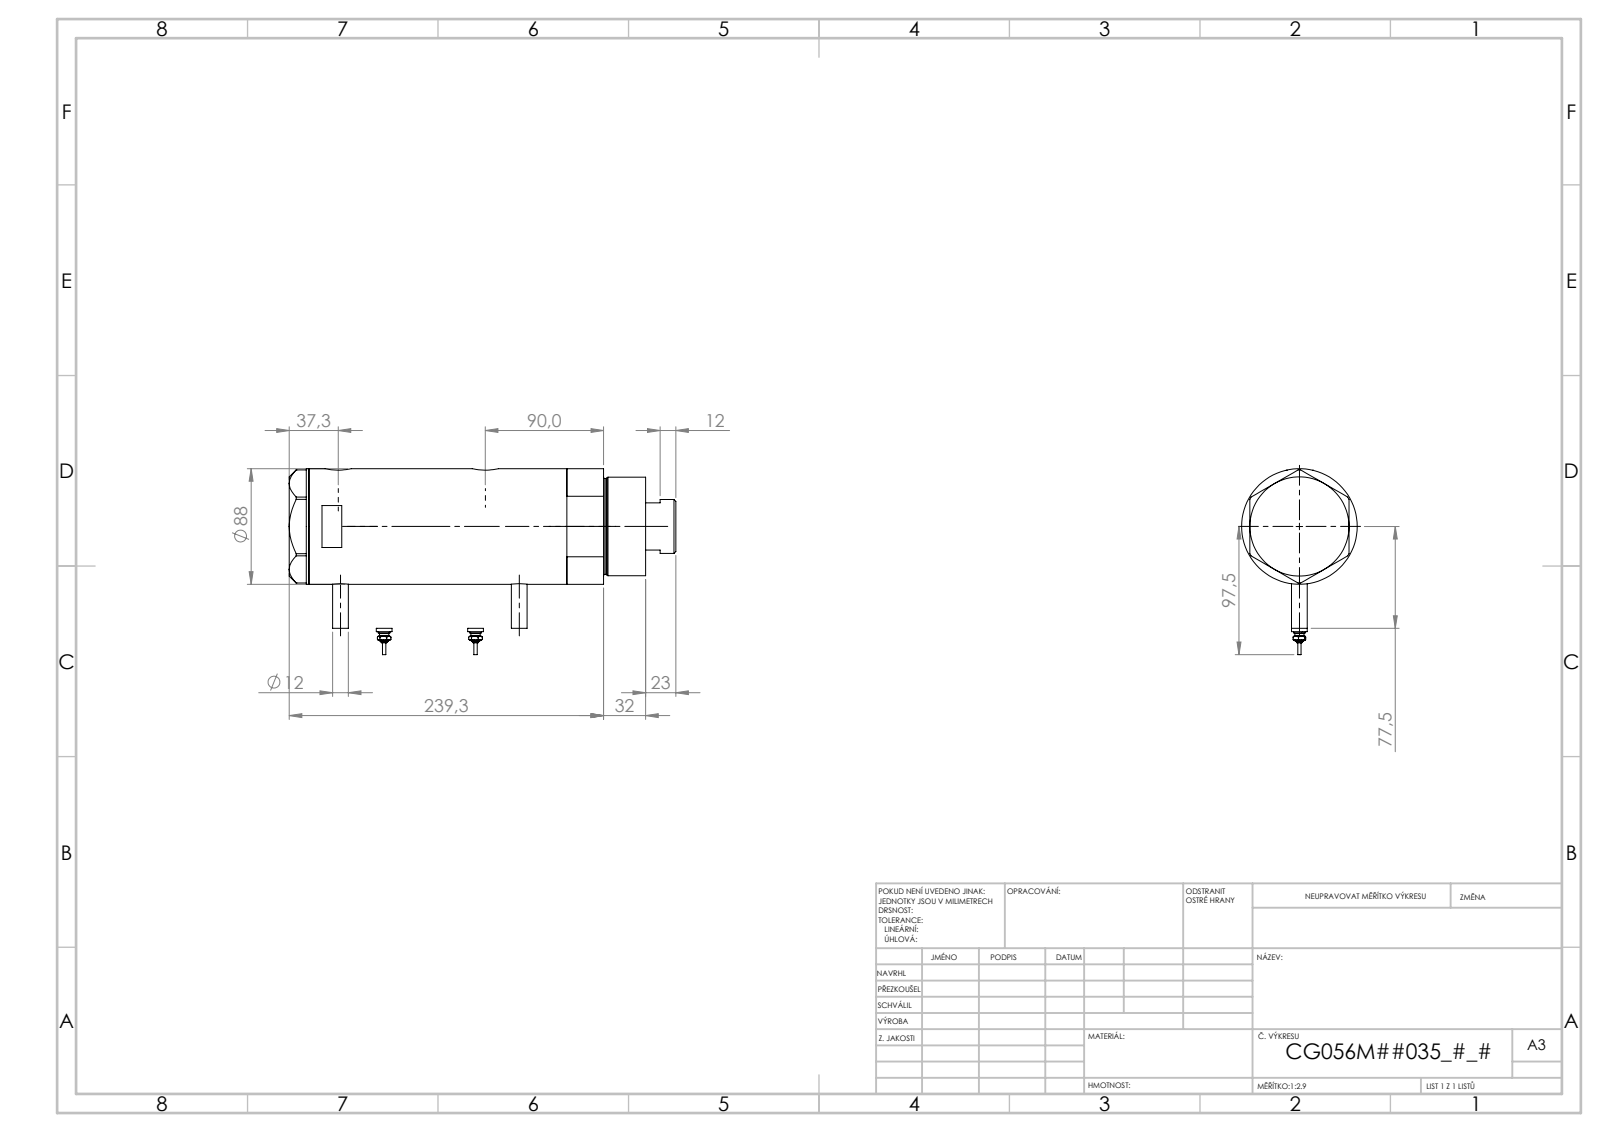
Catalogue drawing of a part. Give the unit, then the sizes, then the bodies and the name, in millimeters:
Units: millimetres
Overall size (bounding box): 259.47 × 120.3 × 88
Round holes (diameter × count): ⌀5 ×2, ⌀12.5 ×2, ⌀13.16 ×2, ⌀20 ×2, ⌀14.5 ×1, ⌀42 ×1, ⌀43.5 ×1, ⌀56 ×1, ⌀60 ×1, ⌀80 ×1
Round bosses / shafts (diameter × count): ⌀12 ×2, ⌀9 ×2, ⌀7 ×2, ⌀4.34 ×2, ⌀2.4 ×2, ⌀88 ×1, ⌀75 ×1, ⌀73 ×1
Main face-to-face distances: 109.4, 26, 83.4, 15, 41, 124.4, 221.47, 236.47, 195.47, 112.07
Hole centre spacings: 1.7, 25.8, 85.3, 87, 111.1, 112.8
Volume: 1 340 000 mm³ · Surface area: 202 658 mm²
Bodies: 6 solids, 232 faces (81 planar, 77 cylindrical, 74 other)
Part name (STEP PRODUCT): V270CG_MIDDLE; V270CG_VC; V270CG_FRONT; V270CG_BACK (+1 more)
STEP written by: SolidWorks 2019 (CONFIG_CONTROL_DESIGN)
